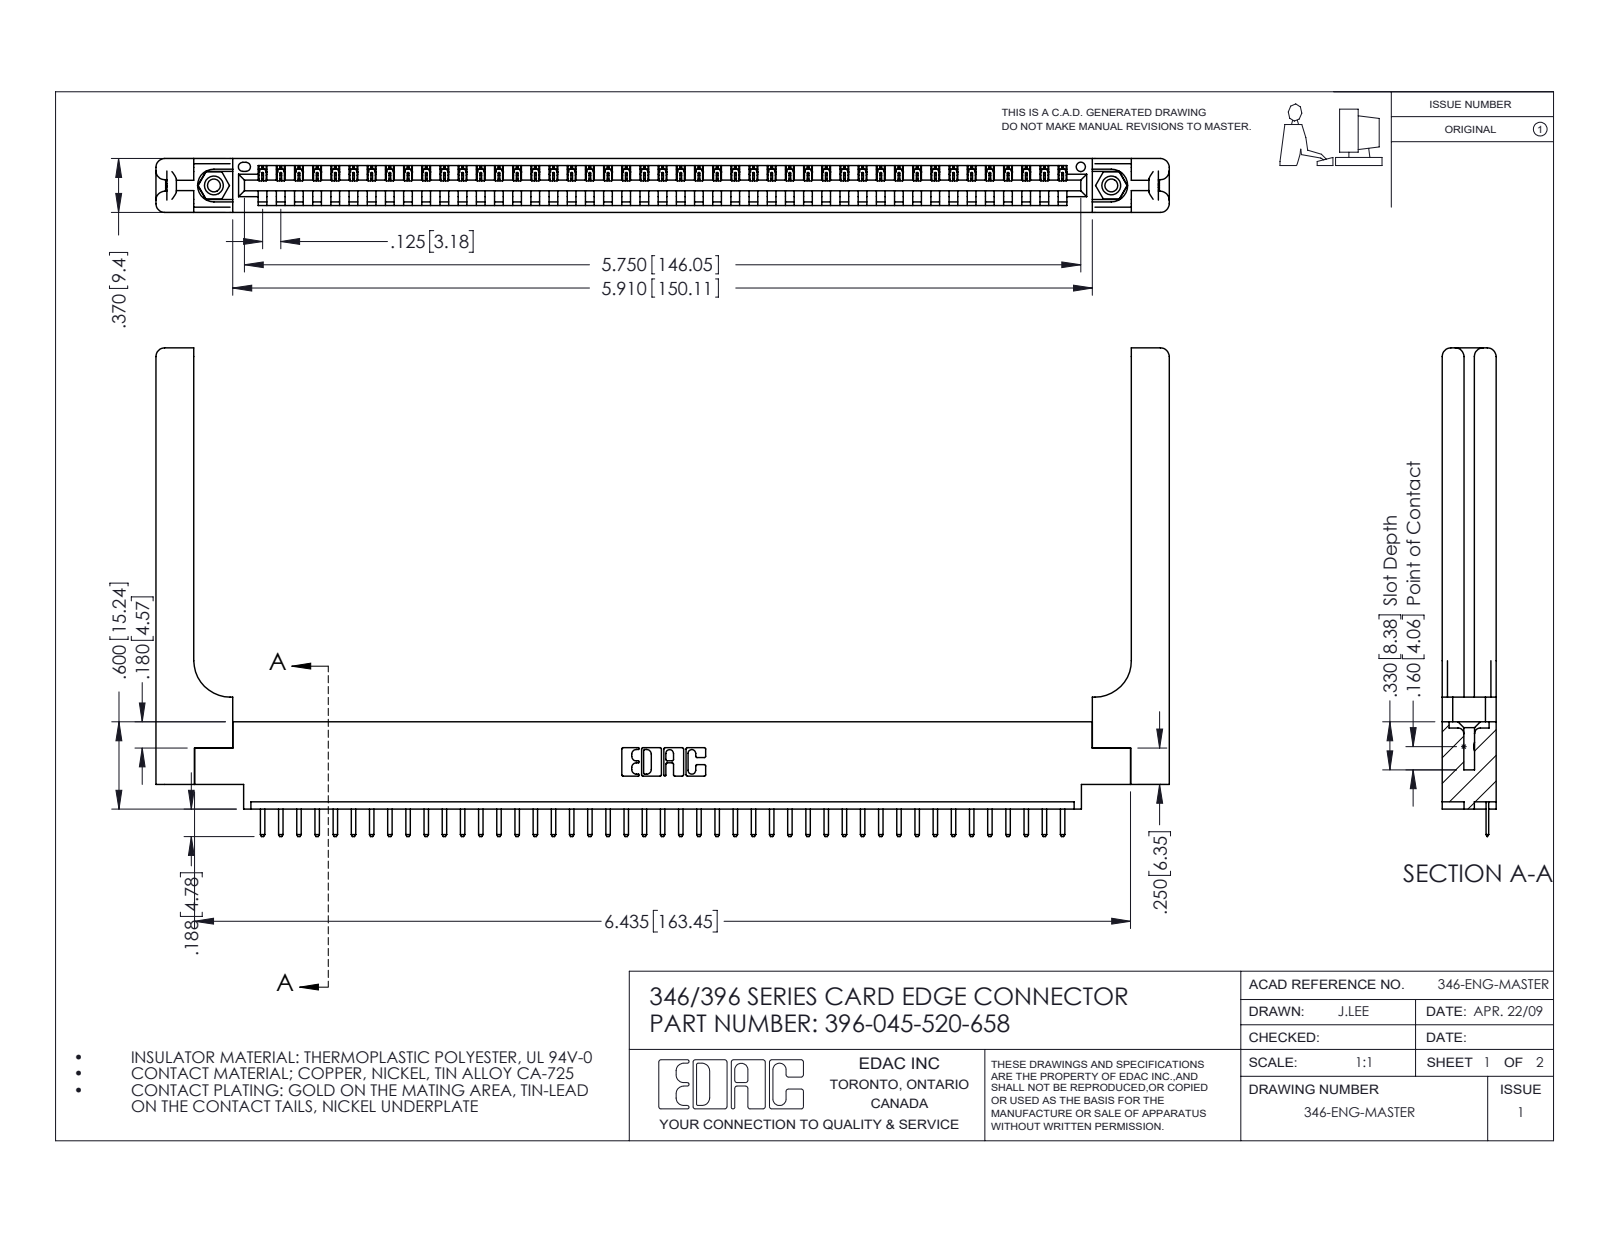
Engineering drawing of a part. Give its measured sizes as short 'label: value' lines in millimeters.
name: 346 Part_0.170 Offset - 0.156 Dia-TH; 345-250-001_345-250-001-102; 345-292-001_345-293-120; 346-220-058_345-220-058 (+1 more)
written by: SolidWorks 2016 (CONFIG_CONTROL_DESIGN)
unit: mm
bodies: 50 solids, 3172 faces (2118 planar, 994 cylindrical, 60 other)
size: 176.9 × 85.3 × 9.4
volume: 24 190 mm³; area: 25 770 mm²
holes: 2× ⌀2.3, 2× ⌀3.2, 2× ⌀4, 1× ⌀1.6
bosses: 2× ⌀3.9
rounds: 92× R0.3, 90× R0.2, 22× R0.3, 16× R1.5, 6× R0.2, 6× R0.8, 3× R0.7, 2× R0.8
face distances: 9.4, 1.2, 8.2, 1.8, 3.8, 3.8, 6.4, 7.6, 0.6, 5.6
hole spacings: 6.2, 151.4, 156.7
